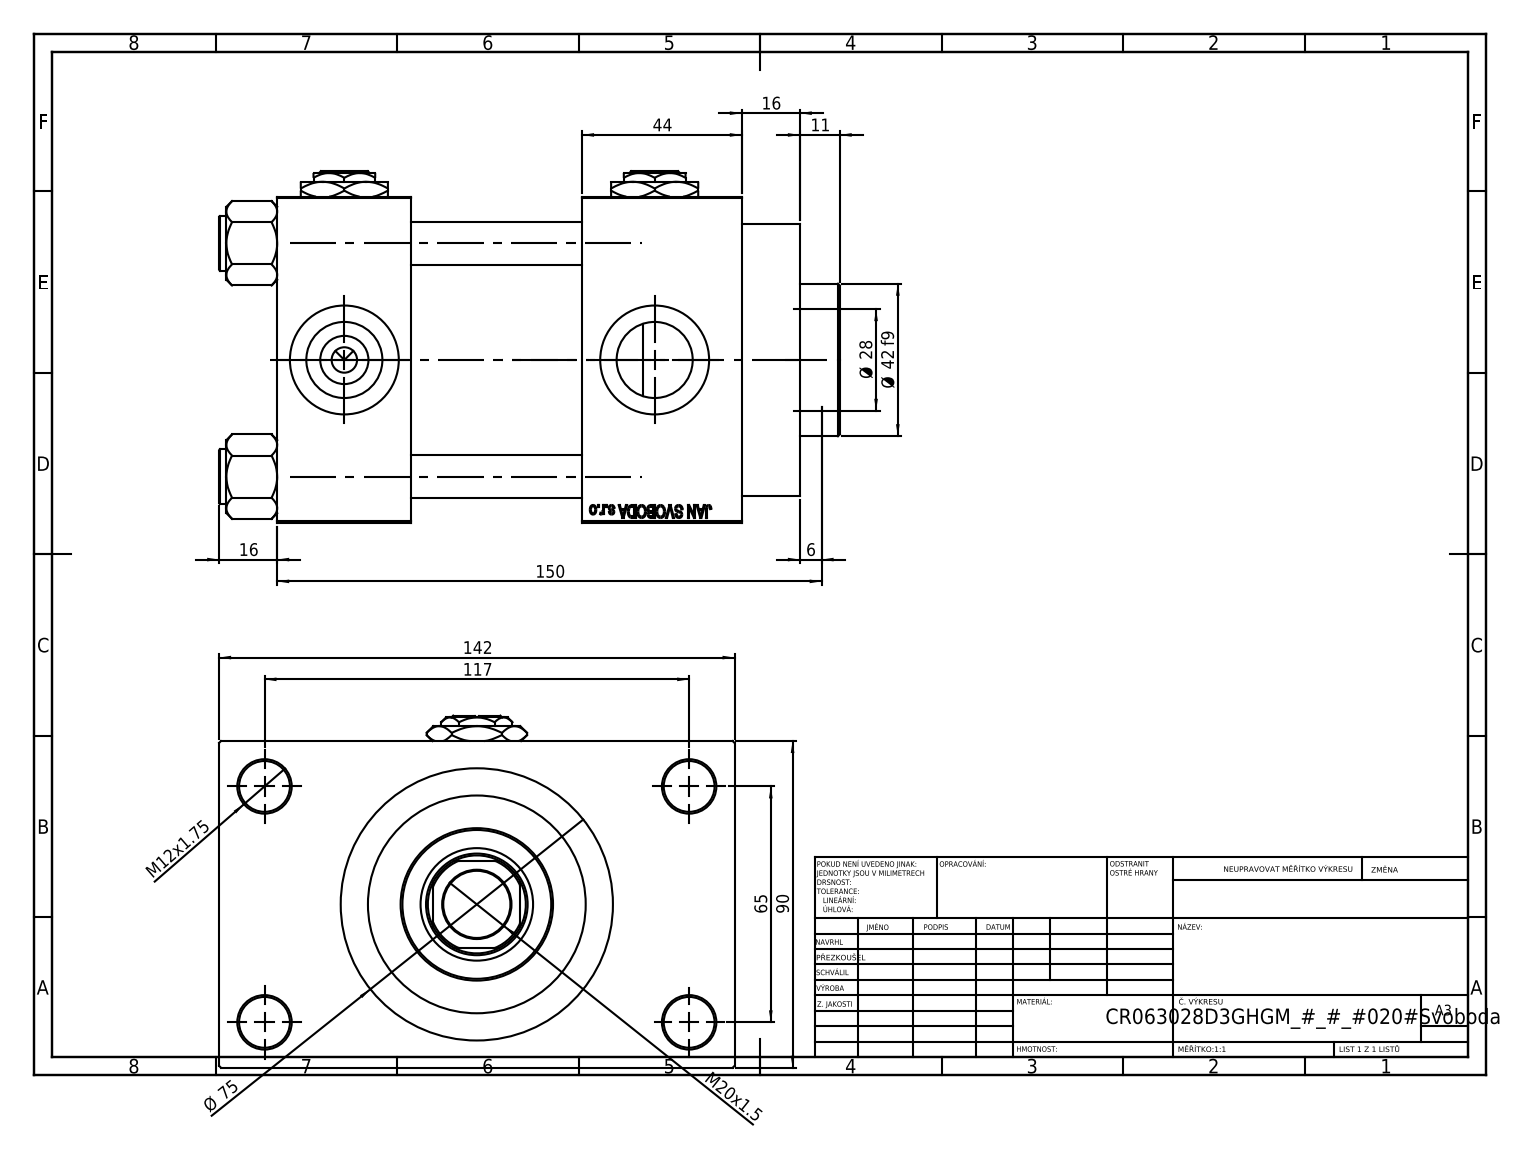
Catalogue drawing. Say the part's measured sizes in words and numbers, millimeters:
The part is named "V215CR_VCP_D; V215CR_D_Body; V215CR_D_TYCINKA; Zatka_pro_OIL_PORT (+2 more)". Its 3-D file was written by "SolidWorks 2019 (CONFIG_CONTROL_DESIGN)". It is 13 solids with 1204 faces: 545 planar, 99 cylindrical and 560 other. Overall it measures 171 by 142 by 97 millimeters. Its volume is 1 015 000 cubic millimeters and its surface area 191 018 square millimeters. Round holes: 4 of diameter 12, 4 of diameter 14, 4 of diameter 20.96, 4 of diameter 30, 3 of diameter 7, 1 of diameter 18.5, 1 of diameter 28, 1 of diameter 31, 1 of diameter 50, 1 of diameter 60, 1 of diameter 63. Round bosses or shafts: 4 of diameter 15, 1 of diameter 75, 1 of diameter 69, 1 of diameter 42. Partial cylindrical surfaces (rounded edges, fillets, slot ends): 1 of radius 13.5. The main face-to-face distances are 90, 47, 37, 84, 91, 128, 44, 26, 116, 64. The hole center spacings are 26.35, 45.47, 64.3, 66.92, 69.81, 90.65, 111.34, 65.
